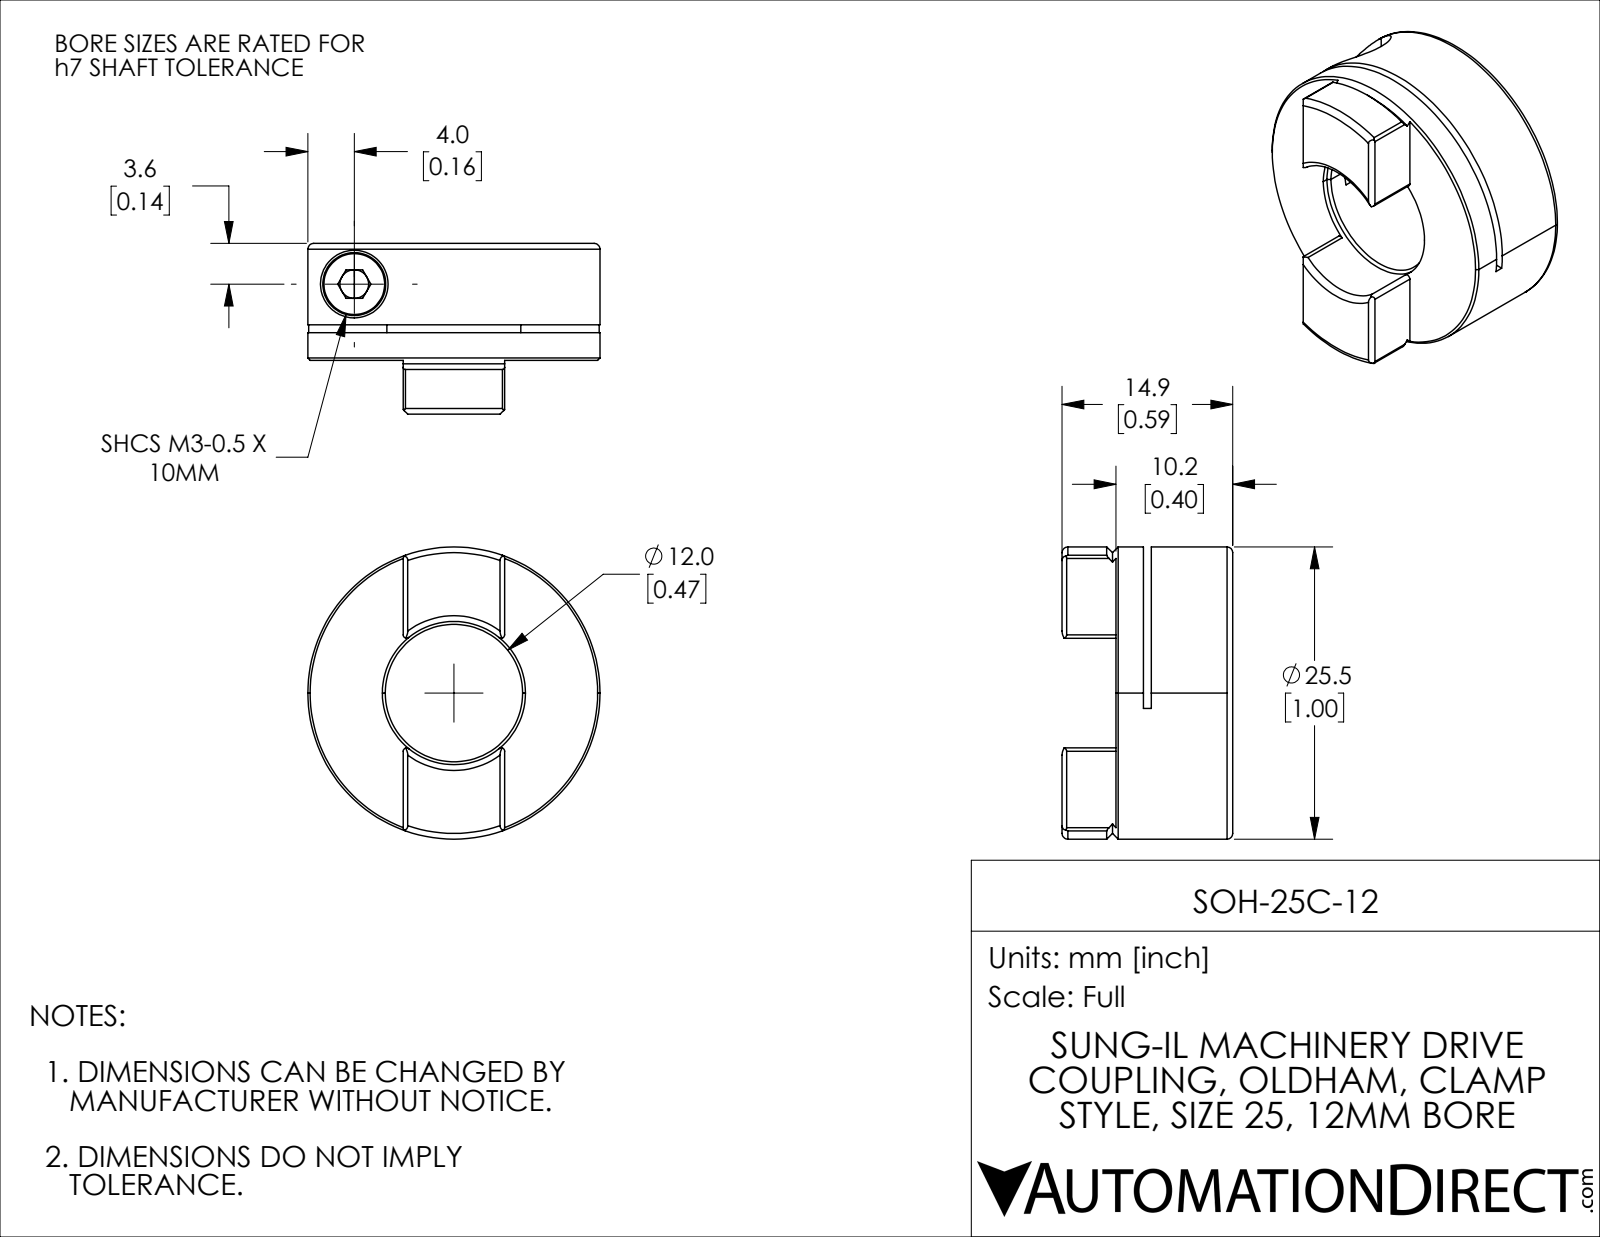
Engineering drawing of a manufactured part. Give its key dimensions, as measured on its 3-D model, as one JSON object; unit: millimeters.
{"part_name": "SOH-25C-12", "step_written_by": "SolidWorks 2021 (CONFIG_CONTROL_DESIGN)", "units": "millimeters", "bodies": {"solids": 2, "faces": 96, "planar": 38, "cylindrical": 33, "other": 25}, "overall_size": [25.5, 25.5, 14.9], "volume_mm3": 4298, "surface_area_mm2": 3113, "round_holes": [[2.5, 1], [3.3, 1], [5.9, 1], [12, 1], [12.5, 1]], "round_bosses_or_shafts": [[25.5, 1], [5.5, 1], [3, 1]], "partial_cylinders_radius": [[0.3, 8], [22.5, 1]], "face_to_face_distances": [7.8, 7.1, 10.2, 2.4, 0.7, 3.1, 14.9, 4.7, 8.86, 0.8]}
